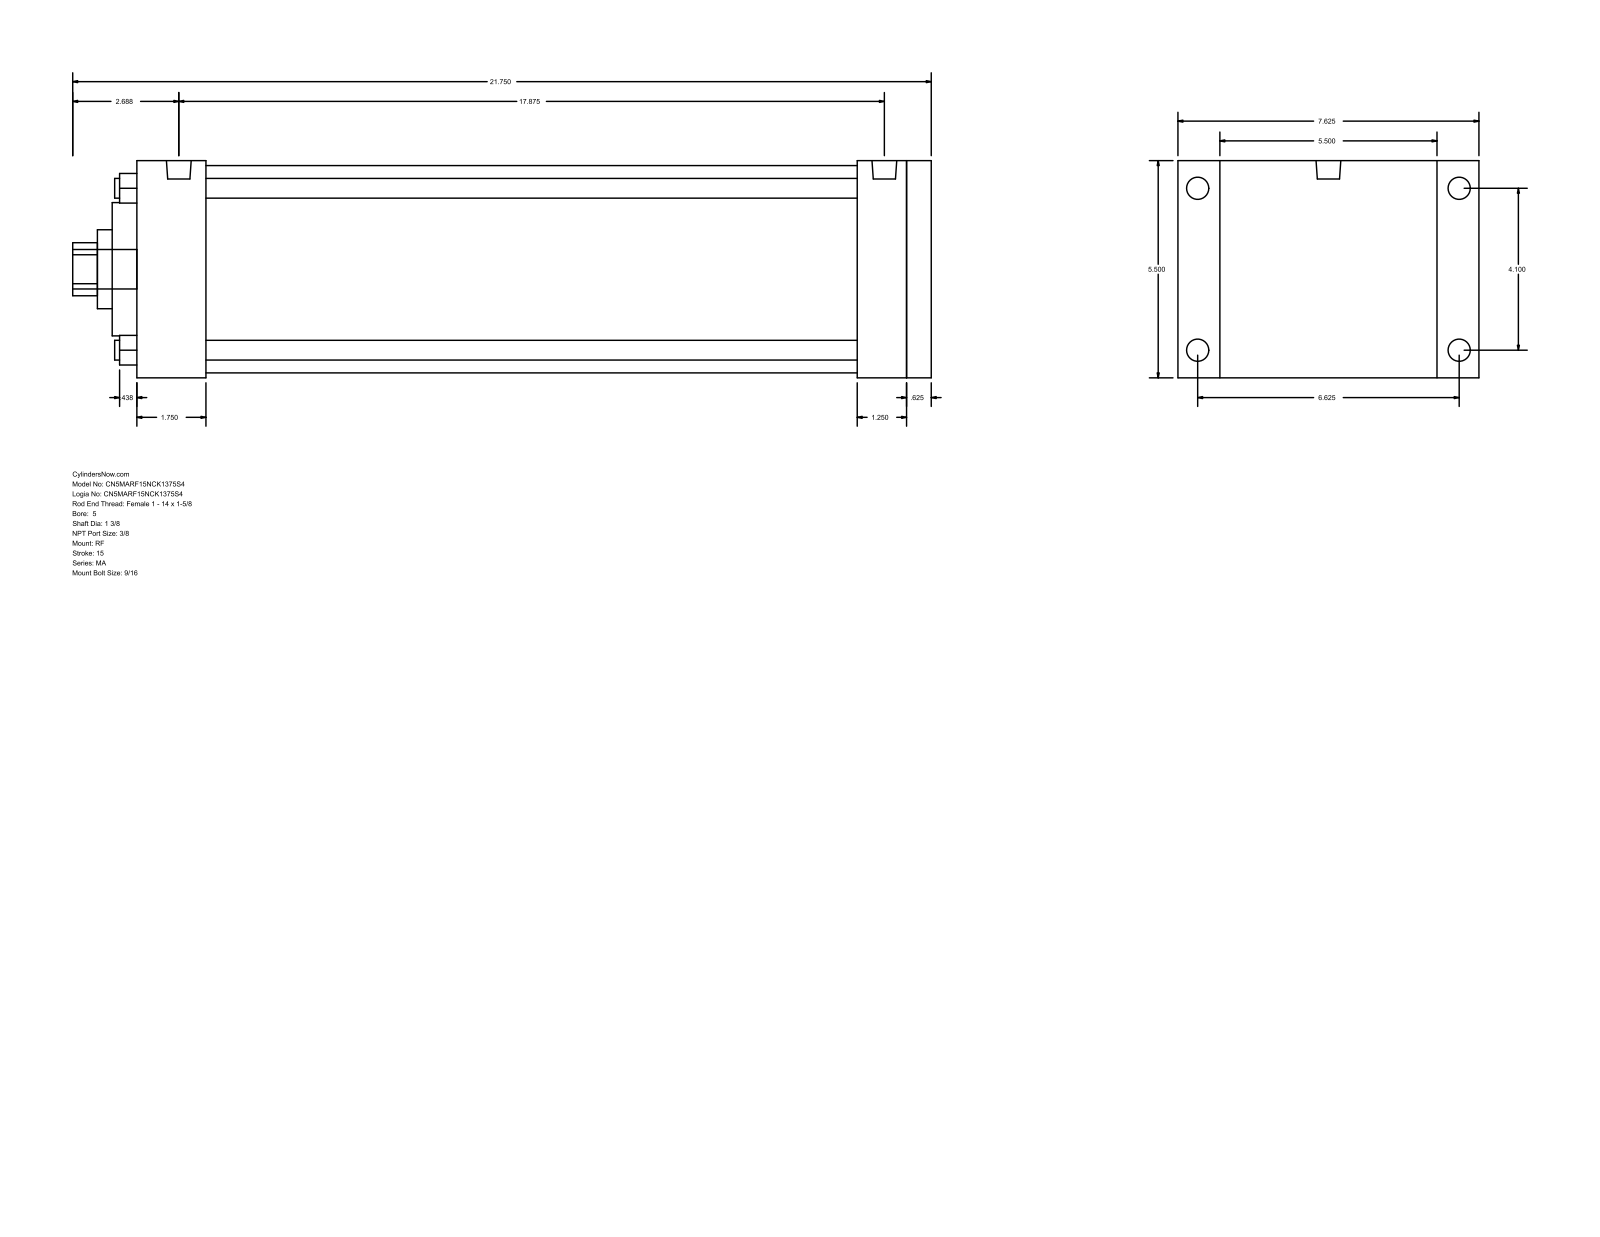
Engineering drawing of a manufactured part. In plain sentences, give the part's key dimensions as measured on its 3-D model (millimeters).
The part is named "MA_RF__0500_1.375". Its 3-D file was written by "GSSL Pune (CONFIG_CONTROL_DESIGN)". It is 0 solids with 94 faces: 65 planar, 29 cylindrical and 0 other. Overall it measures 552.45 by 193.68 by 139.7 millimeters. Round holes: 4 of diameter 12.7, 1 of diameter 34.92, 1 of diameter 50.8, 1 of diameter 85.72, 1 of diameter 133.35. Round bosses or shafts: 4 of diameter 14.29, 4 of diameter 11.11, 2 of diameter 15.93, 1 of diameter 25.4. Partial cylindrical surfaces (rounded edges, fillets, slot ends): 1 of radius 17.06. The main face-to-face distances are 139.7, 511.18, 15.87, 495.31, 44.45, 450.86, 466.73, 463.55, 419.1, 31.76. The hole center spacings are 73.64, 104.14, 147.28.
